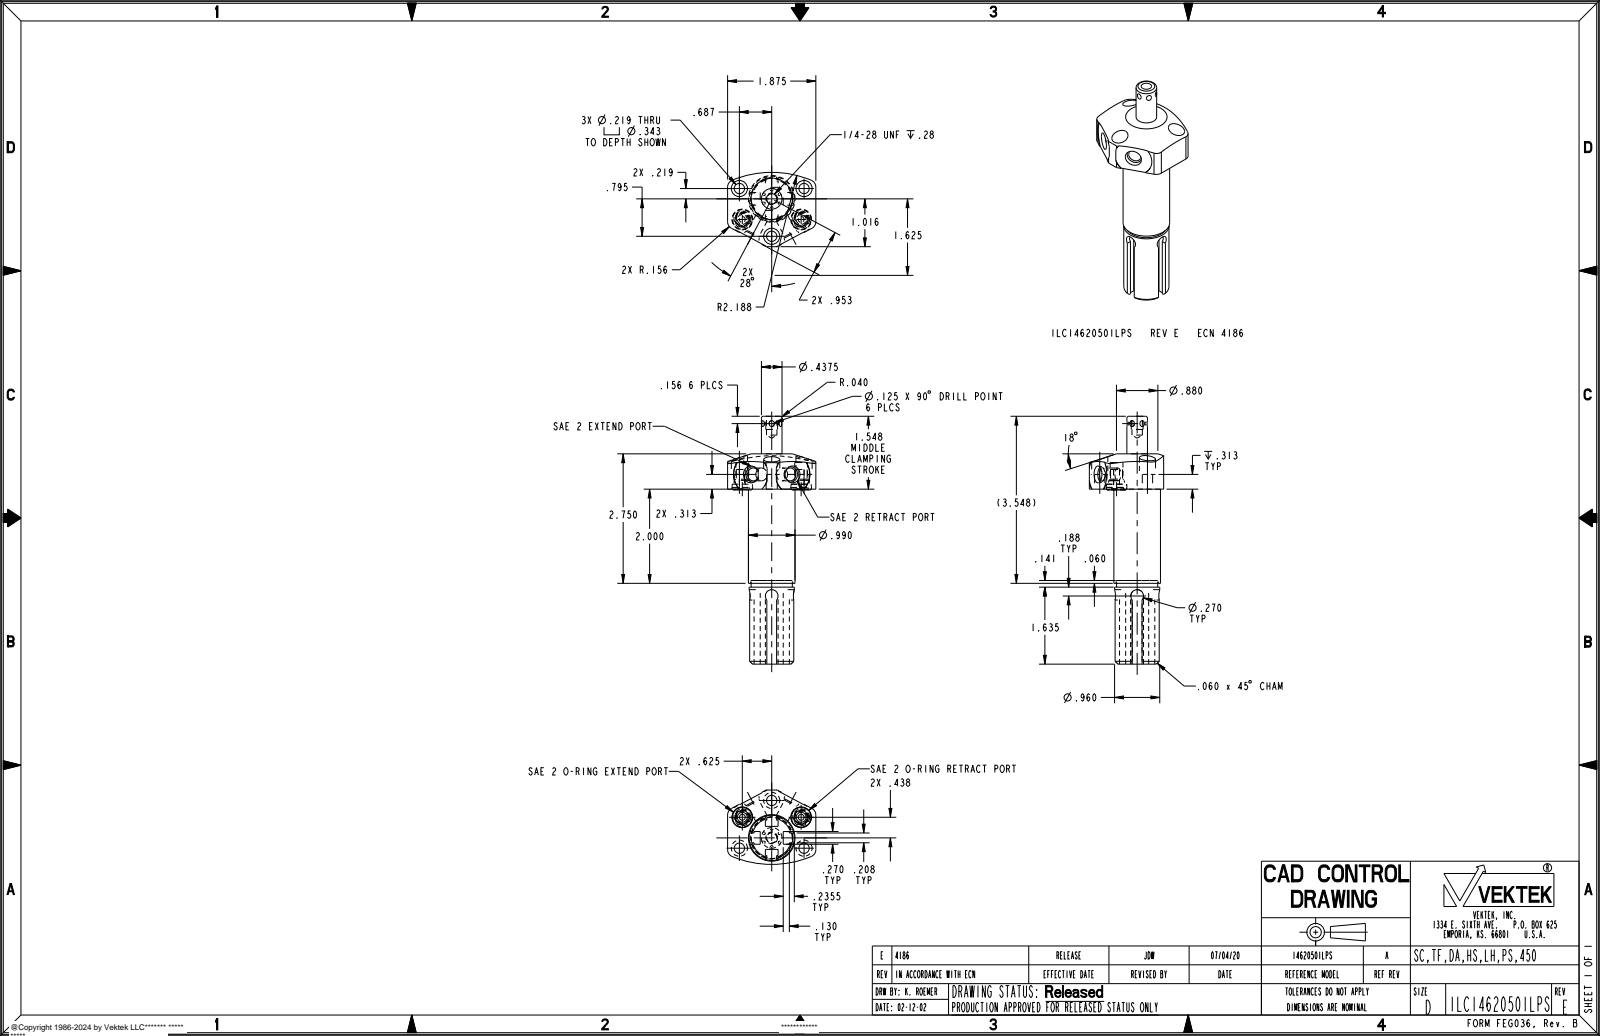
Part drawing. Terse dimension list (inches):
name: ILC14620501LPS
written by: PRO/ENGINEER BY PARAMETRIC TECHNOLOGY CORPORATION, 2013320 (AUTOMOTIVE_DESIGN)
unit: in
bodies: 1 solid, 181 faces (66 planar, 69 cylindrical, 46 other)
size: 5.264 × 1.875 × 1.579
volume: 3.956 in³; area: 30.37 in²
holes: 4× ⌀0.272, 3× ⌀0.219, 3× ⌀0.343, 2× ⌀0.125, 2× ⌀0.438, 1× ⌀0.221, 1× ⌀0.895
bosses: 2× ⌀0.43, 2× ⌀0.256, 2× ⌀0.21, 1× ⌀0.99, 1× ⌀0.96, 1× ⌀0.875, 1× ⌀0.437, 1× ⌀0.25
rounds: 4× R0.156, 2× R0.135, 2× R0.412, 1× R2.188
face distances: 0.109, 0.38, 0.141, 0.348, 0.031, 0.239, 0.489, 0.693, 1.182, 0.802
hole spacings: 0.66, 0.72, 0.721, 0.763, 1.225, 1.468, 0.795, 1.25
